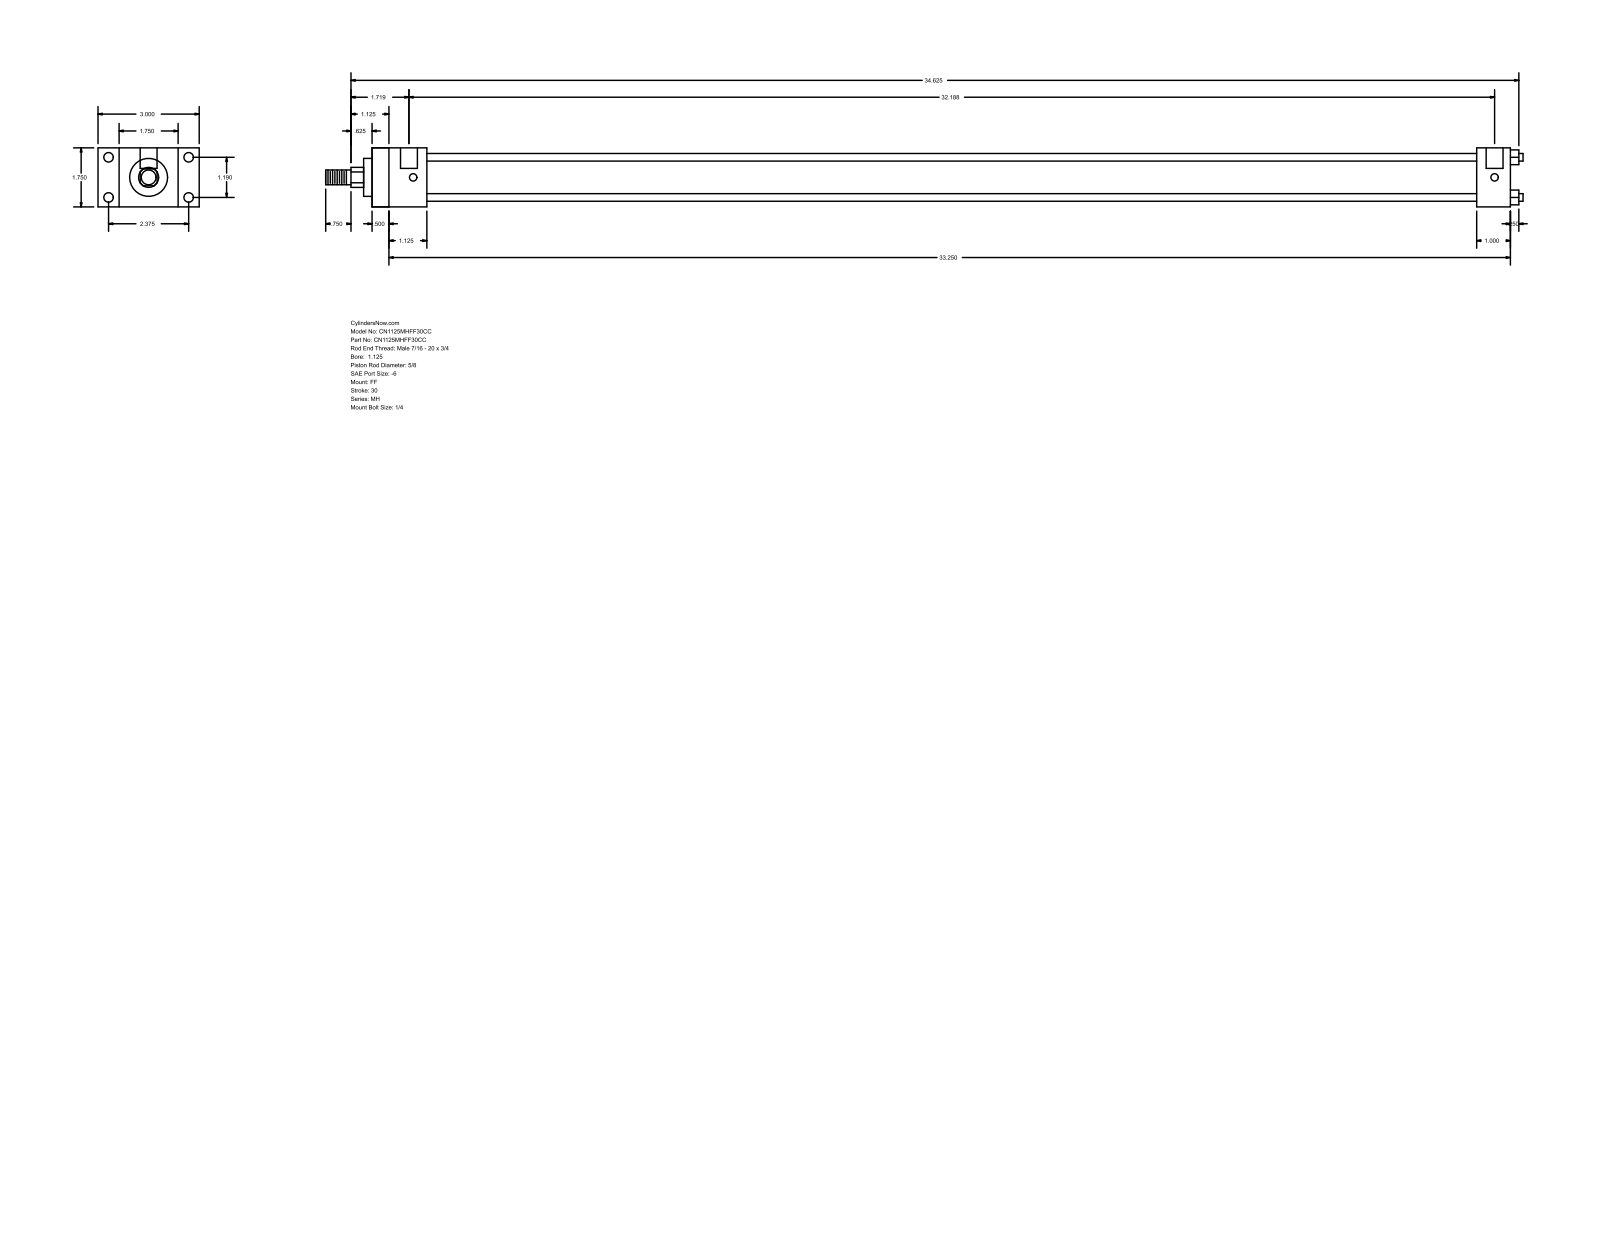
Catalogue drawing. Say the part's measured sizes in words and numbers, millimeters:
The part is named "MH_FF__0112_0.625". Its 3-D file was written by "GSSL Pune (CONFIG_CONTROL_DESIGN)". It is 0 solids with 92 faces: 64 planar, 28 cylindrical and 0 other. Overall it measures 901.7 by 76.2 by 44.45 millimeters. Round holes: 4 of diameter 5.56, 4 of diameter 7.14, 2 of diameter 12.7. Round bosses or shafts: 4 of diameter 5.71, 1 of diameter 34.92, 1 of diameter 28.57, 1 of diameter 15.88, 1 of diameter 11.11. Partial cylindrical surfaces (rounded edges, fillets, slot ends): 1 of radius 7.54. The main face-to-face distances are 44.46, 857.24, 12.69, 844.55, 15.87, 28.58, 60.33, 41.27, 831.85, 819.16. The hole center spacings are 30.22, 60.32, 67.47, 814.39, 3.17, 817.56.
